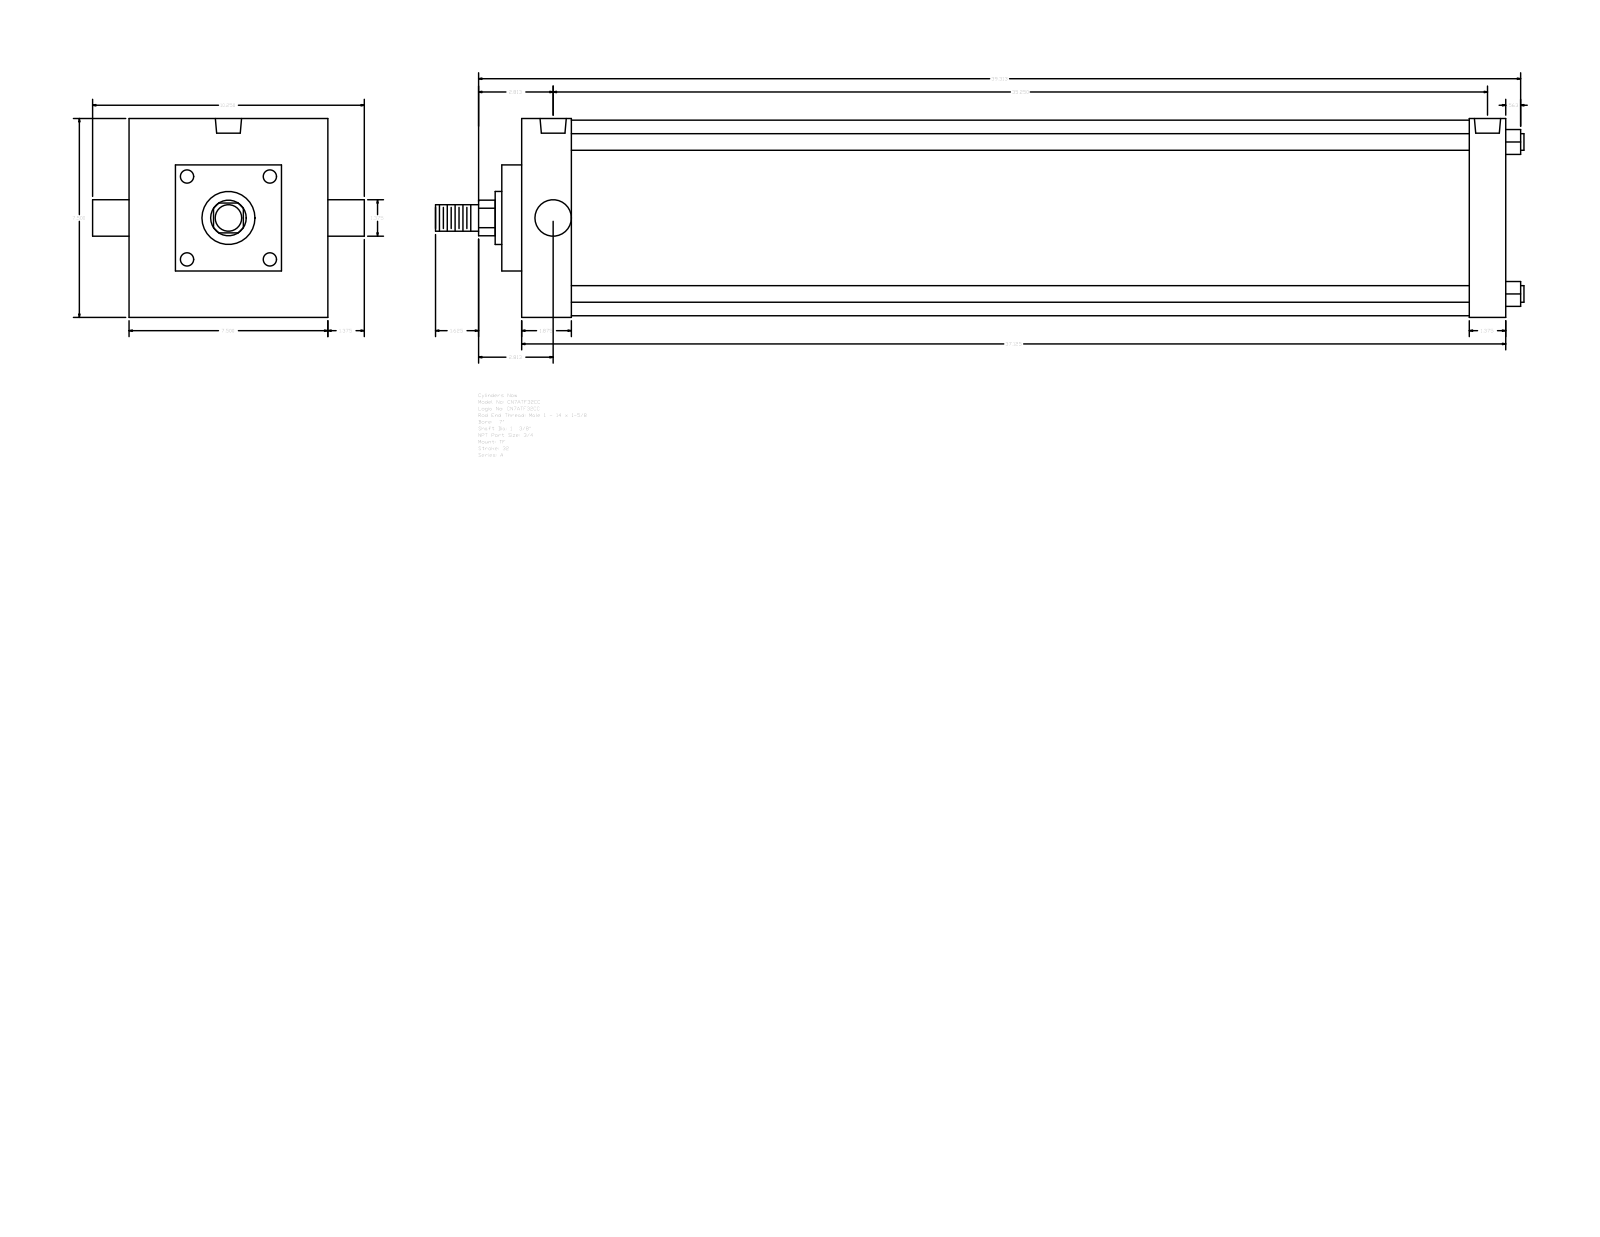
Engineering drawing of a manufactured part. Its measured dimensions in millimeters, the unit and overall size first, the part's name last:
Units: millimetres
Overall size (bounding box): 1042.99 × 260.35 × 190.5
Round holes (diameter × count): ⌀15.08 ×3, ⌀25.12 ×2
Round bosses / shafts (diameter × count): ⌀15.88 ×4, ⌀34.92 ×2, ⌀187.32 ×1, ⌀50.8 ×1, ⌀25.4 ×1
Partial cylindrical surfaces — rounded edges, fillets, slot ends (radius × count): R17.06 ×1
Main face-to-face distances: 190.5, 942.98, 19.04, 962.02, 66.67, 47.63, 895.35, 927.1, 908.06, 860.43
Hole centre spacings: 5.56, 889.79, 884.23, 895.35
Bodies: 0 solids, 89 faces (65 planar, 24 cylindrical, 0 other)
Part name (STEP PRODUCT): A_TF__0700_1.375
STEP written by: GSSL Pune (CONFIG_CONTROL_DESIGN)
